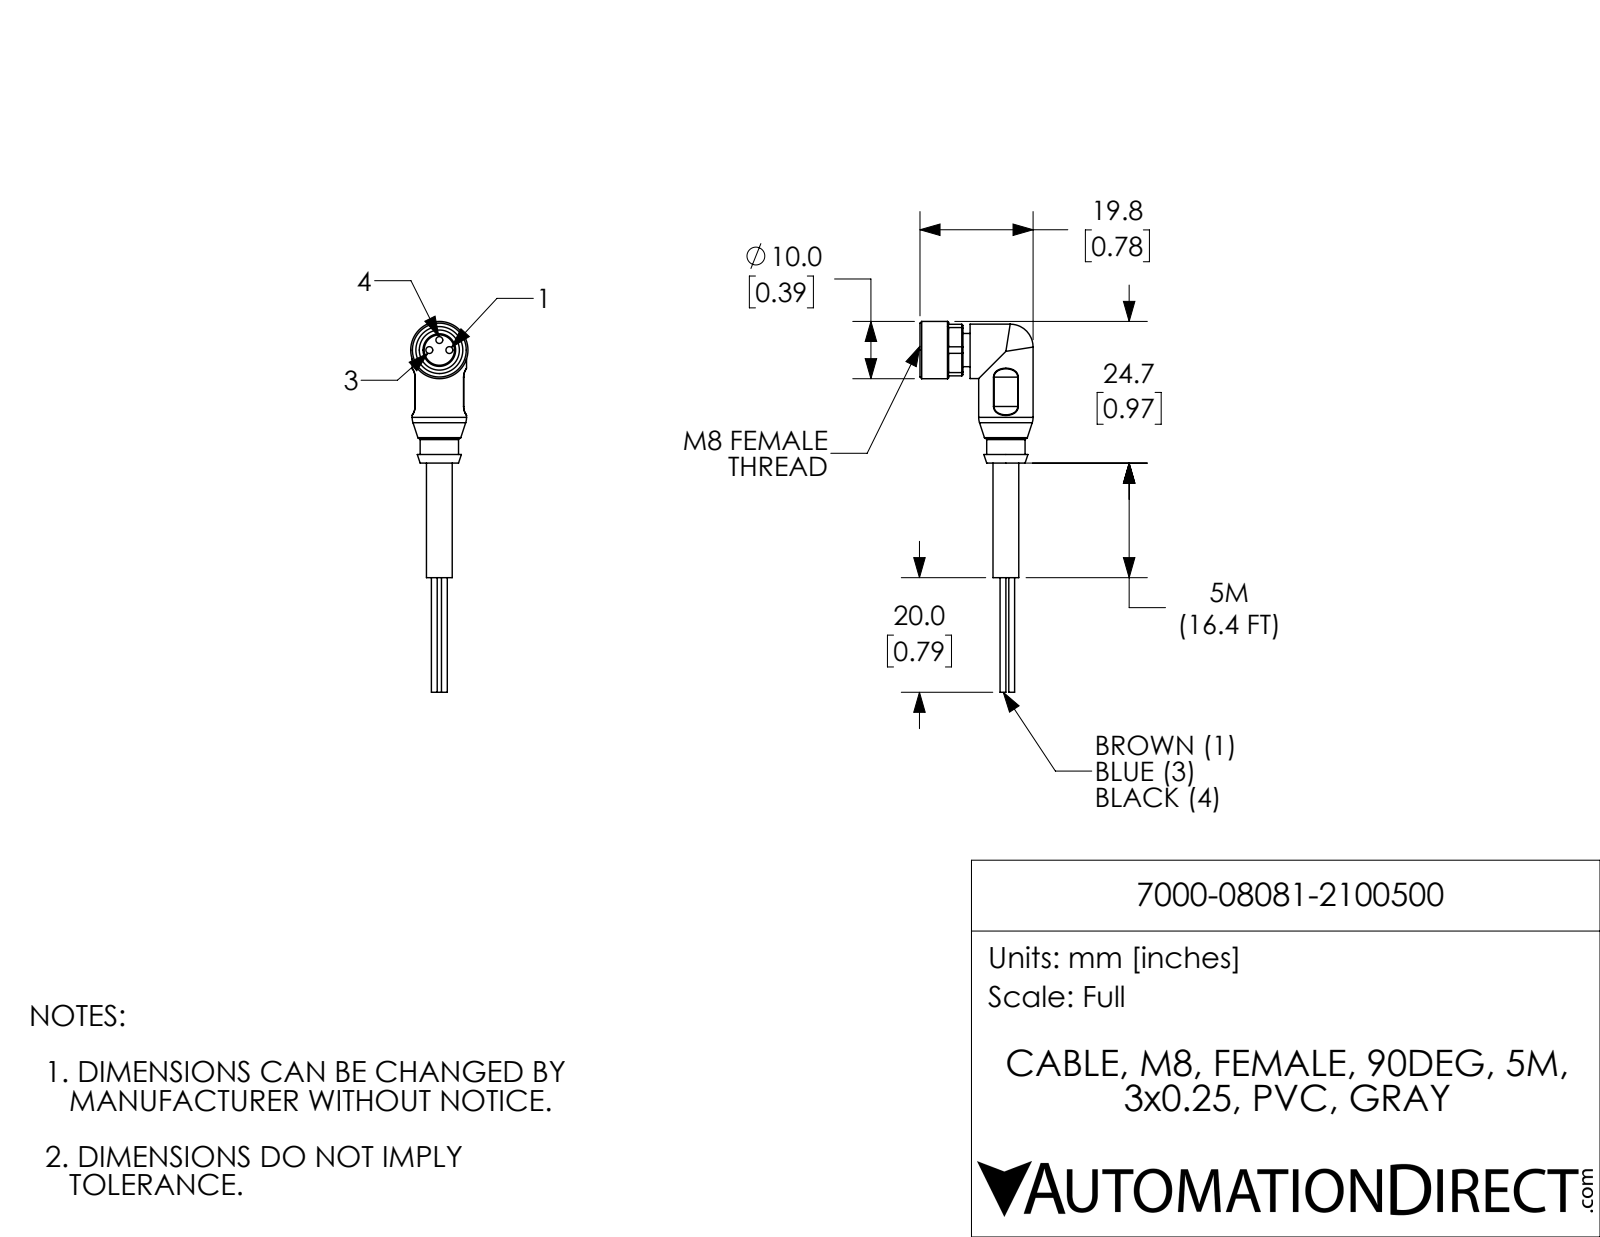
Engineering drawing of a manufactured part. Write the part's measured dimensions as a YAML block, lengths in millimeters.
part_name: "7000-08081-2100500"
step_written_by: "SolidWorks 2017 (AUTOMOTIVE_DESIGN)"
units: millimeters
bodies: {solids: 1, faces: 107, planar: 35, cylindrical: 43, other: 29}
overall_size: [64.7, 19.8, 10]
volume: 2440
surface_area: 1930
round_holes:
  - {diameter: 1.2, count: 3}
  - {diameter: 7, count: 1}
round_bosses_or_shafts:
  - {diameter: 1, count: 3}
  - {diameter: 9.5, count: 2}
  - {diameter: 10, count: 1}
  - {diameter: 6.7, count: 1}
  - {diameter: 5.8, count: 1}
  - {diameter: 5.7, count: 1}
  - {diameter: 4.5, count: 1}
partial_cylinders:
  - {radius: 0.2, count: 4}
  - {radius: 2.5, count: 4}
  - {radius: 4.9, count: 1}
face_to_face_distances: [1.2, 9, 1.5, 8.5, 0.7, 6.8, 8.1, 7.5, 8.7, 20]
hole_center_spacings: [1.8, 2.5, 3.5]
